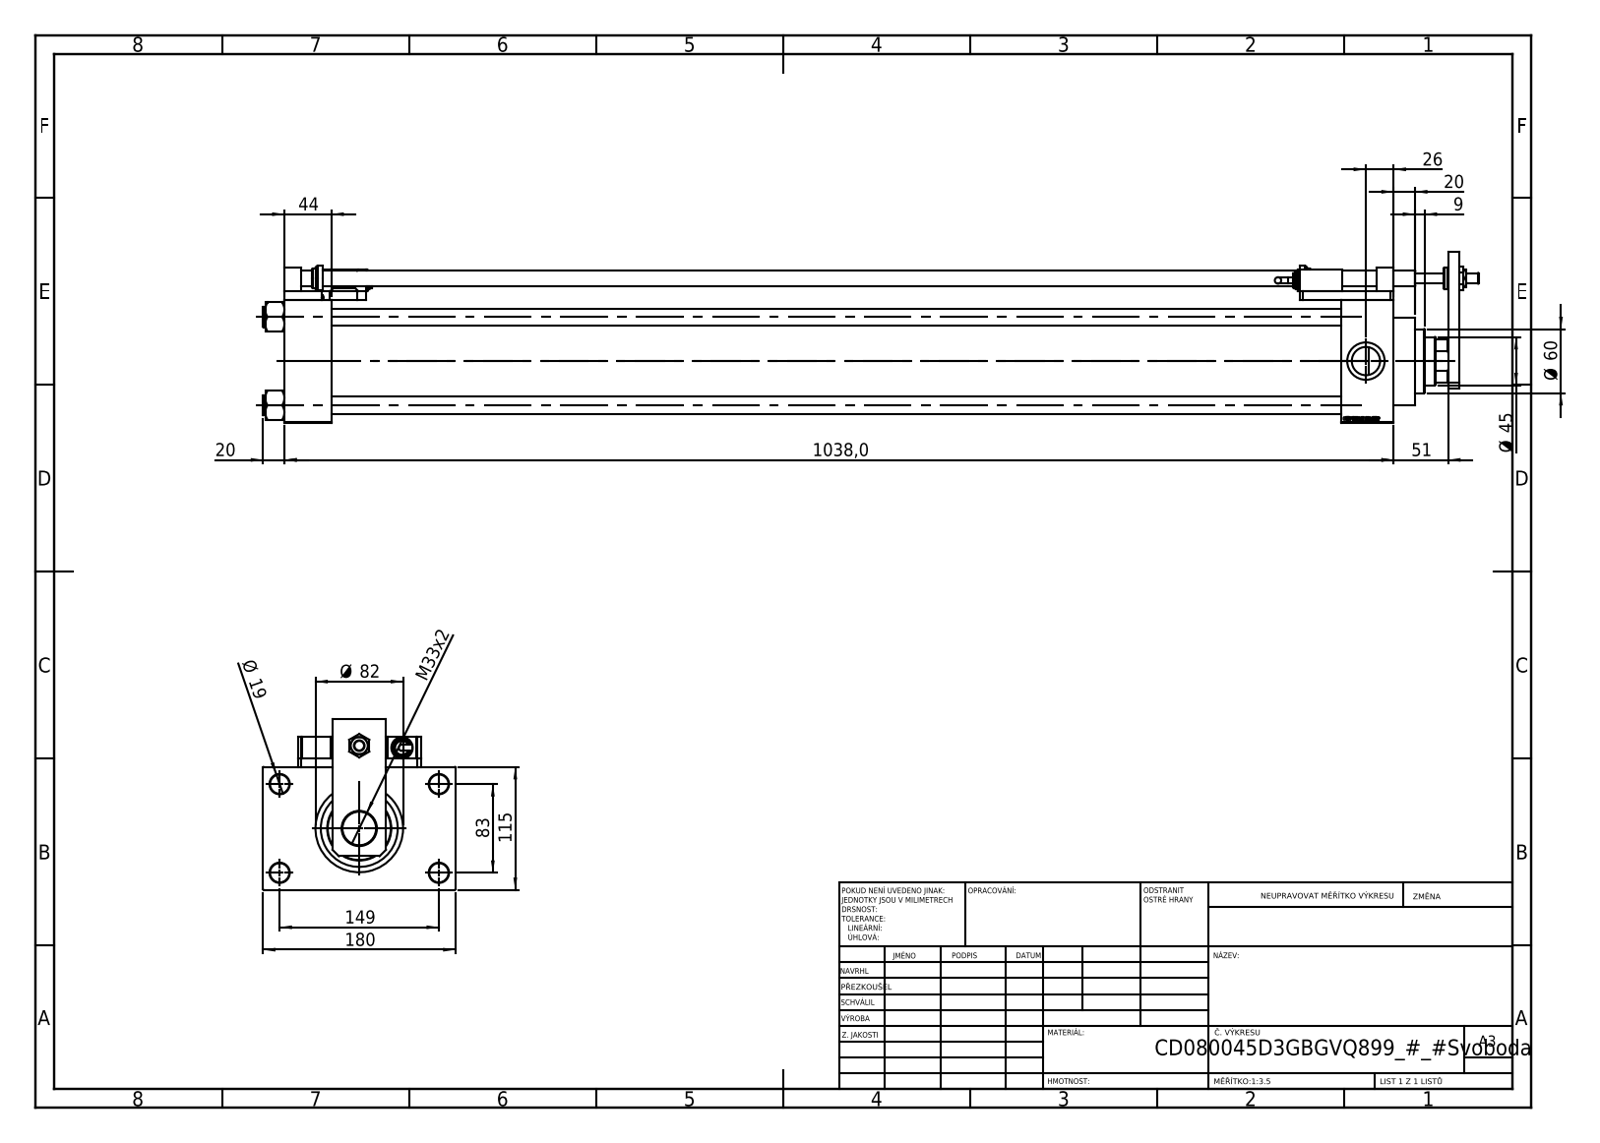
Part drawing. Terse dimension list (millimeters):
name: V215CD_SWITCH_Q_MAGNET; V215CD_SWITCH_Q_DIMA; V215CD_SWITCH_Q_NUT; V215CD_SWITCH_Q_BLOK (+7 more)
written by: SolidWorks 2019 (CONFIG_CONTROL_DESIGN)
unit: mm
bodies: 26 solids, 1480 faces (714 planar, 167 cylindrical, 599 other)
size: 1137.5 × 180 × 160
volume: 5 210 000 mm³; area: 1 198 000 mm²
holes: 4× ⌀8.5, 4× ⌀13.5, 4× ⌀16, 4× ⌀18, 4× ⌀26.44, 4× ⌀35, 3× ⌀7, 1× ⌀10, 1× ⌀14, 1× ⌀31.5, 1× ⌀33, 1× ⌀45
bosses: 4× ⌀19, 3× ⌀20, 2× ⌀16, 2× ⌀14, 2× ⌀6, 1× ⌀86, 1× ⌀82, 1× ⌀60
rounds: 4× R7.5, 1× R22
face distances: 115, 8, 49, 44, 994, 1038, 989, 945, 123, 32.5
hole spacings: 33.15, 58.48, 82.7, 85.28, 89.24, 115.85, 142.43, 21.26
